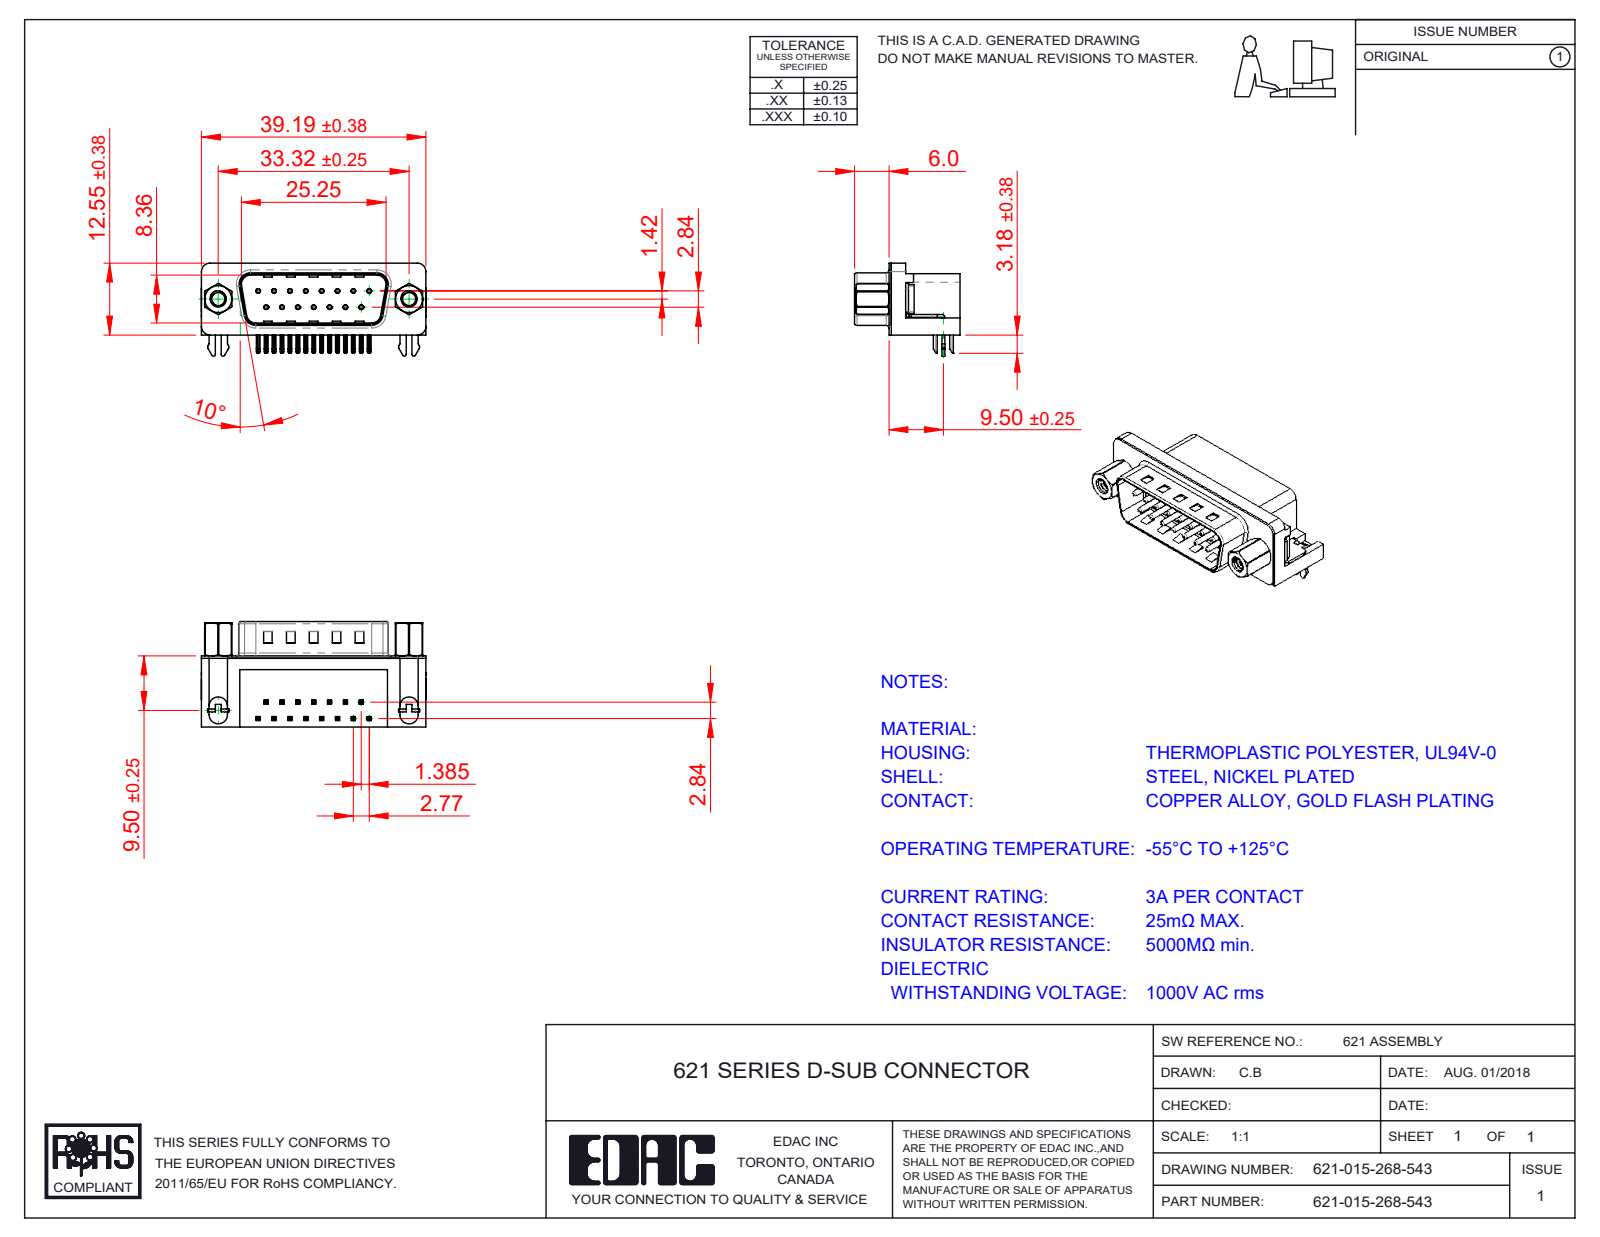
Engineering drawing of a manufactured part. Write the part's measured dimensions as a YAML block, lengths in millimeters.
part_name: "621 Housing_15 Socket; 621 Shell_15 Socket; 621 4 Prong Board Lock; 621 4-40 Hex Standoff 5 (+4 more)"
step_written_by: "SolidWorks 2016 (CONFIG_CONTROL_DESIGN)"
units: millimeters
bodies: {solids: 23, faces: 1723, planar: 957, cylindrical: 523, other: 243}
overall_size: [39.22, 18.4, 16.25]
volume: 4638
surface_area: 6208
round_holes:
  - {diameter: 0.35, count: 15}
  - {diameter: 0.8, count: 15}
  - {diameter: 2, count: 2}
  - {diameter: 2.26, count: 2}
  - {diameter: 2.29, count: 2}
  - {diameter: 4, count: 2}
  - {diameter: 4.8, count: 2}
  - {diameter: 5, count: 2}
round_bosses_or_shafts:
  - {diameter: 0.75, count: 15}
  - {diameter: 4.9, count: 2}
  - {diameter: 4.75, count: 2}
  - {diameter: 3.9, count: 2}
  - {diameter: 3, count: 2}
  - {diameter: 2.79, count: 2}
partial_cylinders:
  - {radius: 0.25, count: 72}
  - {radius: 0.12, count: 30}
  - {radius: 1, count: 16}
  - {radius: 0.5, count: 9}
  - {radius: 1.6, count: 8}
  - {radius: 1.5, count: 6}
  - {radius: 0.9, count: 4}
  - {radius: 2, count: 4}
face_to_face_distances: [0.4, 12, 10.35, 12.4, 2.1, 10.46, 1.7, 10.86, 8.76, 9.5]
hole_center_spacings: [3.16, 2.77, 5.54, 8.31, 11.08, 5.03, 5.04, 7.48]
